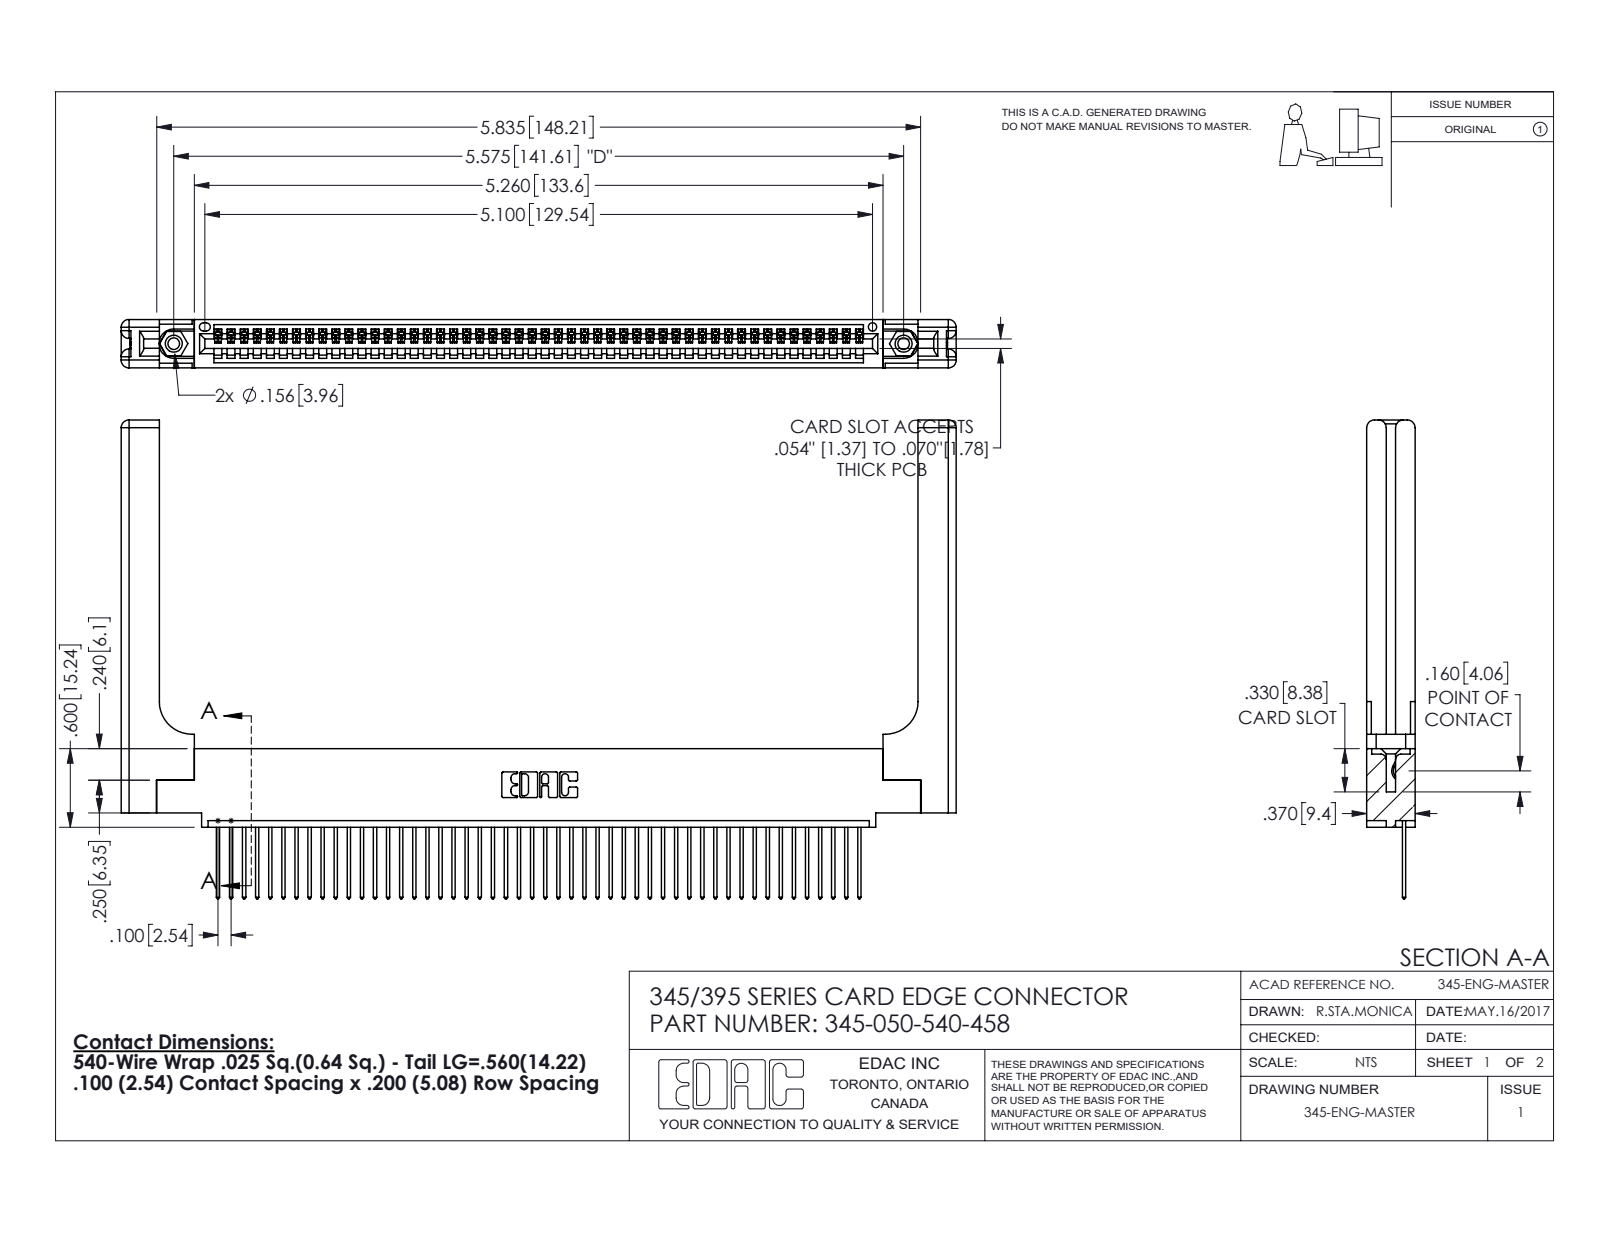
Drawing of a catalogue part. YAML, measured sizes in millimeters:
part_name: "345-220-058_345-220-058; 345-250-001_345-250-001-102; 345-292-001_345-293-140; 345 Part_0.110 Offset - 0.156 Dia-TH (+1 more)"
step_written_by: "SolidWorks 2016 (CONFIG_CONTROL_DESIGN)"
units: millimeters
bodies: {solids: 55, faces: 3286, planar: 2232, cylindrical: 994, other: 60}
overall_size: [162, 92.9, 9.4]
volume: 23960
surface_area: 26520
round_holes:
  - {diameter: 2.3, count: 2}
  - {diameter: 3.2, count: 2}
  - {diameter: 4, count: 2}
  - {diameter: 1.6, count: 1}
round_bosses_or_shafts:
  - {diameter: 3.9, count: 2}
partial_cylinders:
  - {radius: 0.2, count: 100}
  - {radius: 0.3, count: 100}
  - {radius: 0.3, count: 22}
  - {radius: 1.5, count: 16}
  - {radius: 0.2, count: 6}
  - {radius: 0.8, count: 6}
  - {radius: 0.7, count: 3}
  - {radius: 0.8, count: 2}
face_to_face_distances: [1.8, 7.6, 9.4, 2.5, 6.9, 0.6, 5.1, 5.7, 3.8, 3.8]
hole_center_spacings: [6.9, 135.6, 141.6]
